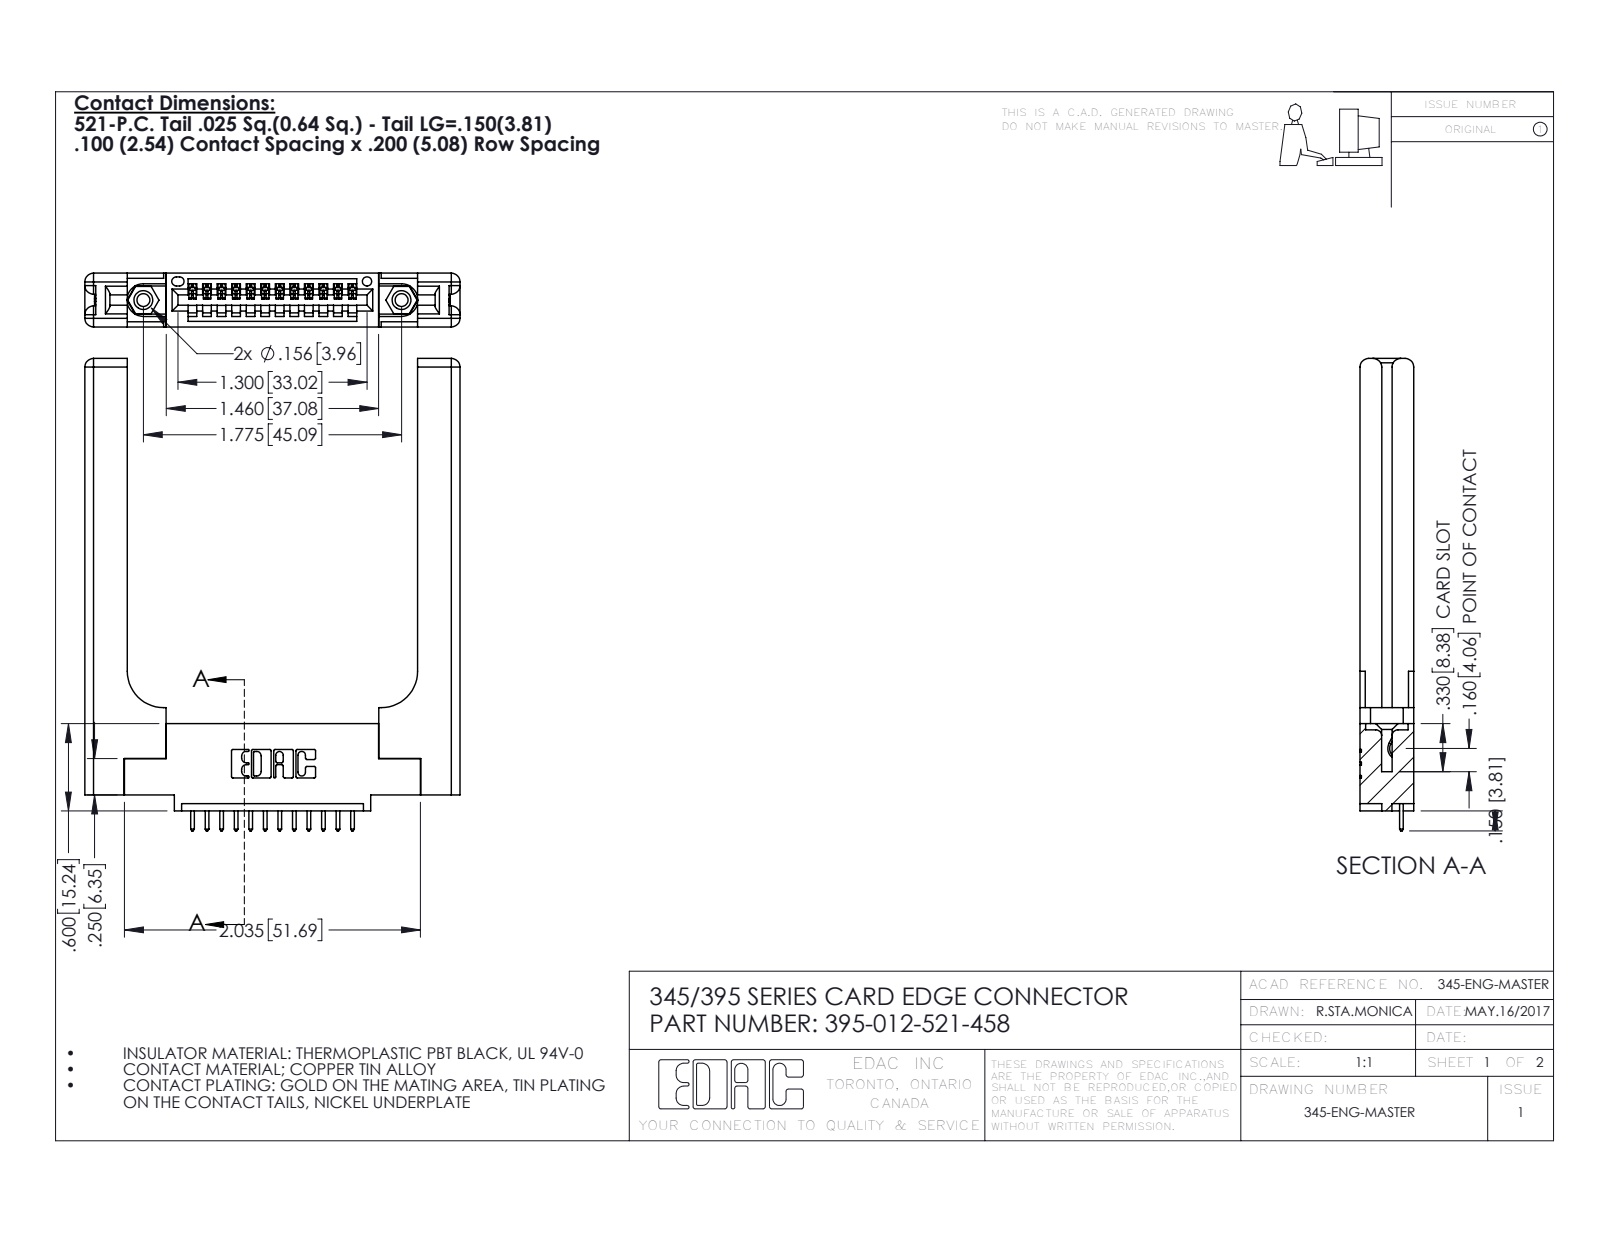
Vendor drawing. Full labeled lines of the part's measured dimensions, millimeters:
Part name (STEP PRODUCT): 345-292-001_345-293-121; 395-012-521-458; 345-220-058_345-220-058; 345 Part_0.110 Offset - 0.156 Dia-TH (+1 more)
STEP written by: SolidWorks 2016 (CONFIG_CONTROL_DESIGN)
Units: millimetres
Bodies: 17 solids, 1082 faces (712 planar, 310 cylindrical, 60 other)
Overall size (bounding box): 82.5 × 65.5 × 9.4
Volume: 14 400 mm³ · Surface area: 12 650 mm²
Round holes (diameter × count): ⌀2.3 ×2, ⌀3.2 ×2, ⌀4 ×2, ⌀1.6 ×1
Round bosses / shafts (diameter × count): ⌀3.9 ×2
Partial cylindrical surfaces — rounded edges, fillets, slot ends (radius × count): R0.2 ×24, R0.3 ×24, R0.3 ×22, R1.5 ×16, R0.2 ×6, R0.8 ×6, R0.7 ×3, R0.8 ×2
Main face-to-face distances: 9.4, 1.8, 3.8, 5.6, 3.8, 2, 7.6, 50.7, 1.8, 5.1
Hole centre spacings: 6.9, 39.2, 45.1
